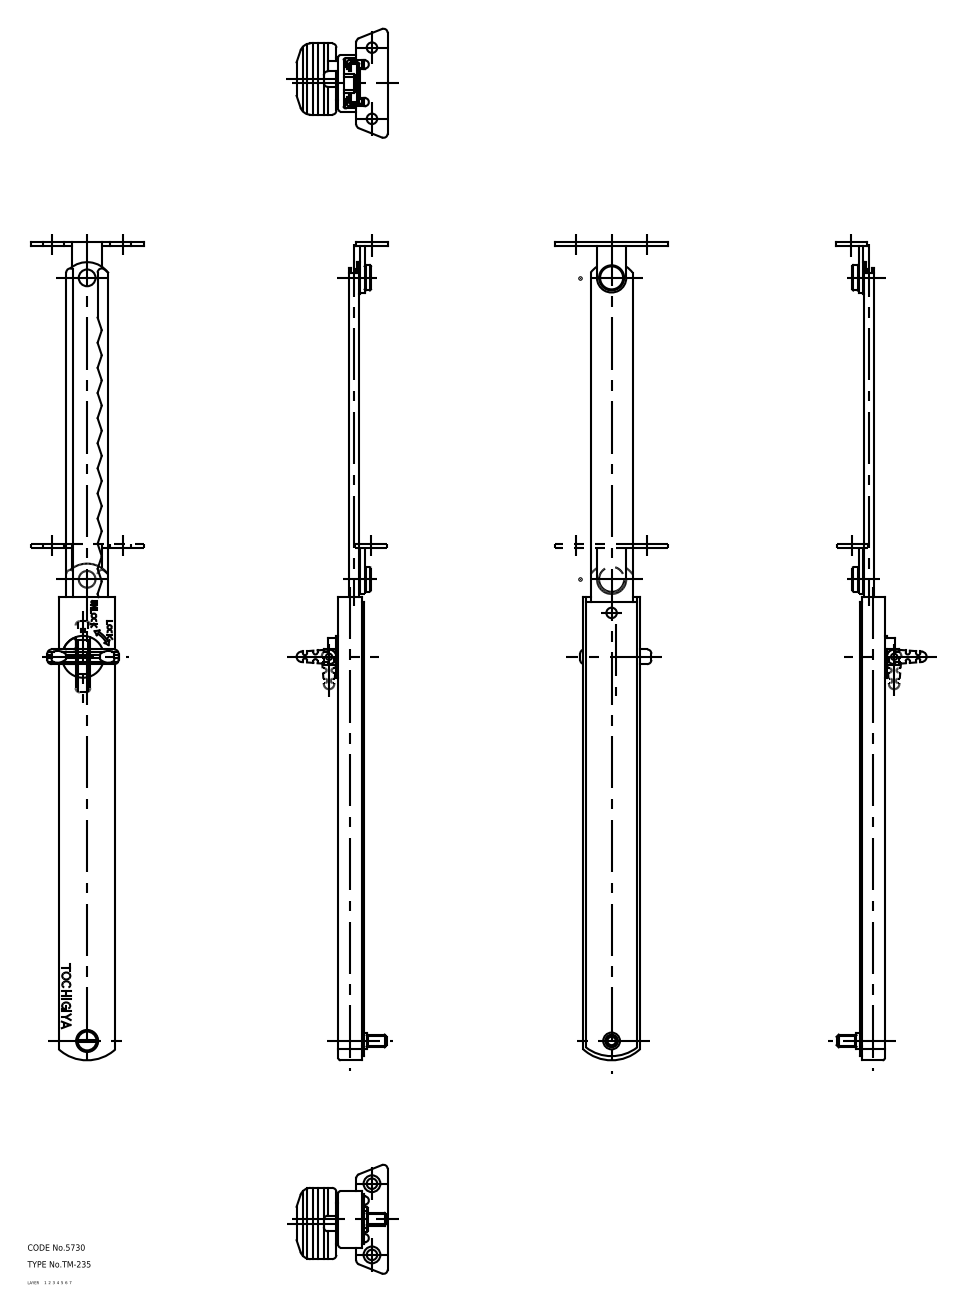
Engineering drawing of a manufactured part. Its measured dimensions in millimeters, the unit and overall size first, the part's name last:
Units: millimetres
Overall size (bounding box): 246.74 × 52.09 × 43.5
Volume: 40 880 mm³ · Surface area: 62 596 mm²
Bodies: 11 solids, 319 faces (0 planar, 0 cylindrical, 319 other)
Part name (STEP PRODUCT): guide_B; washer; rivet; pin (+8 more)
STEP written by: CADfix (AUTOMOTIVE_DESIGN)
